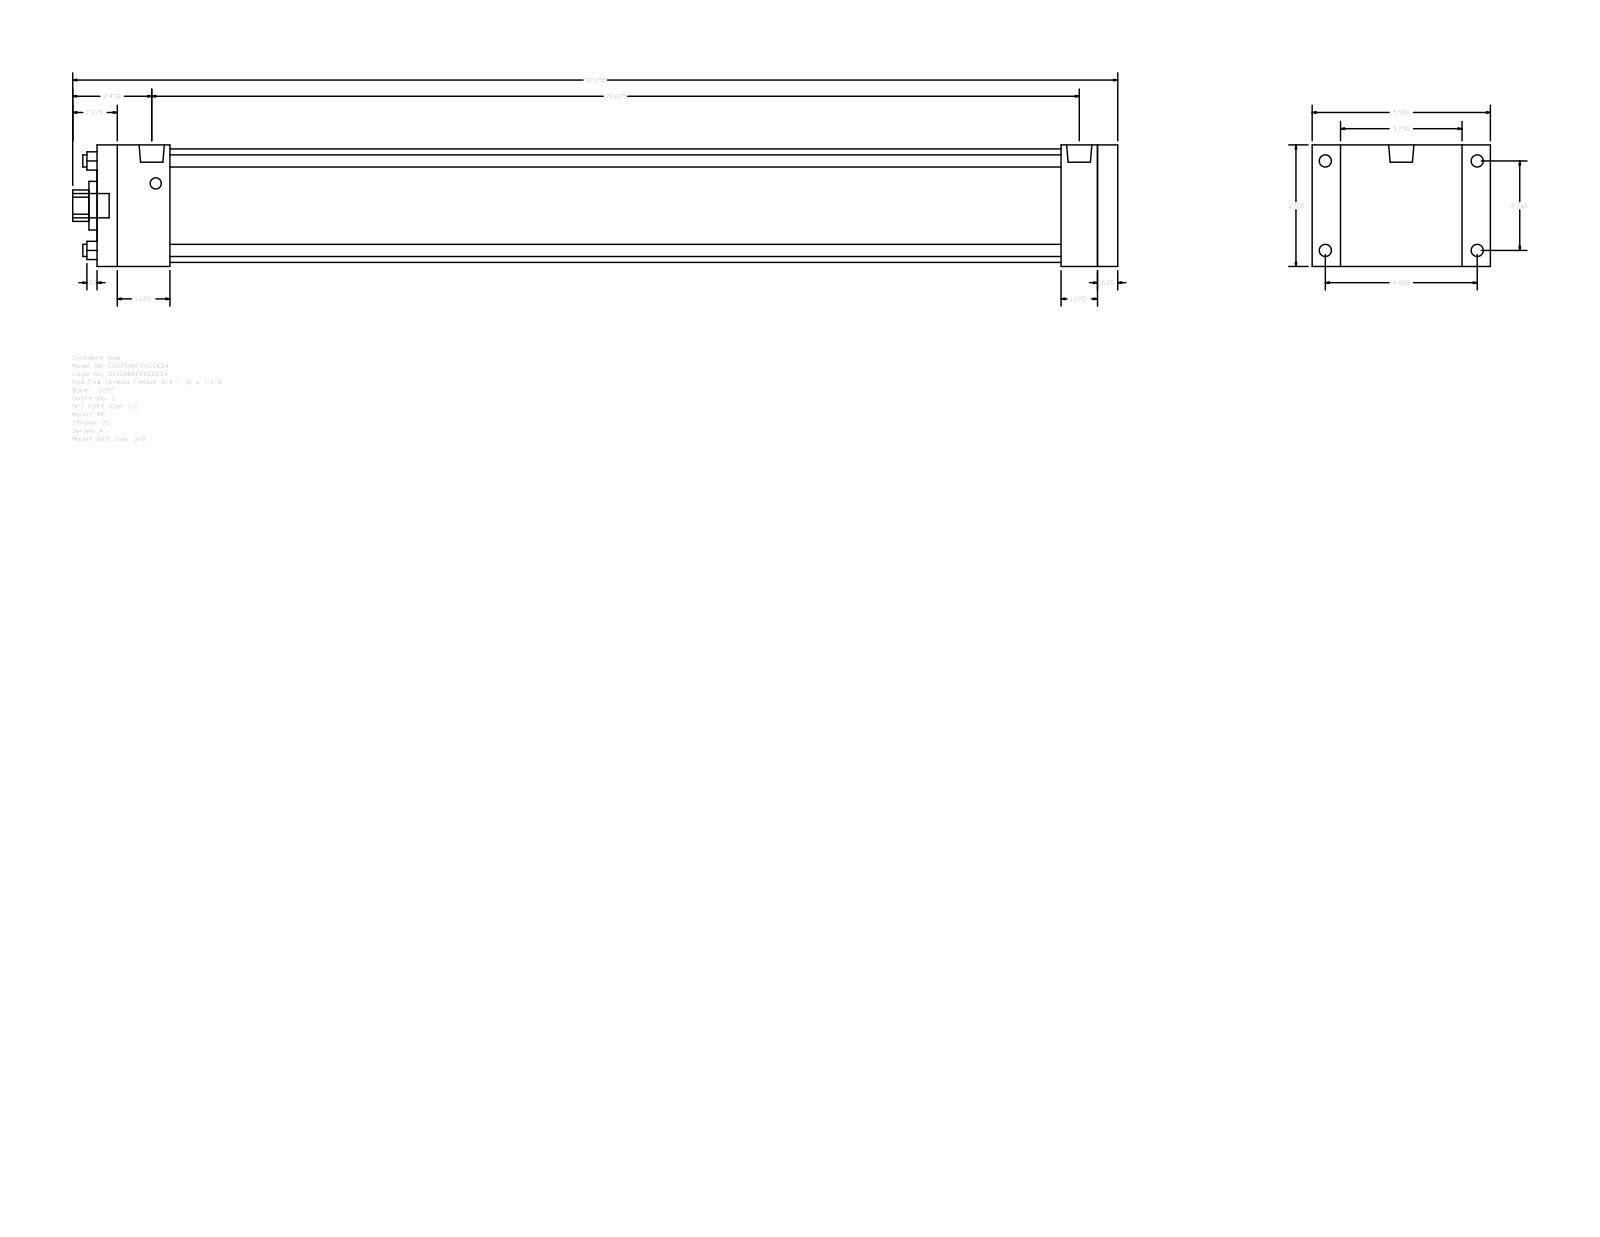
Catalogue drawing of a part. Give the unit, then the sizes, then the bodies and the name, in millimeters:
Units: millimetres
Overall size (bounding box): 819.15 × 139.7 × 95.25
Round holes (diameter × count): ⌀9.53 ×4, ⌀25.4 ×1, ⌀38.1 ×1, ⌀88.9 ×1
Round bosses / shafts (diameter × count): ⌀9.53 ×4, ⌀8.73 ×4, ⌀19.77 ×2, ⌀19.05 ×1
Partial cylindrical surfaces — rounded edges, fillets, slot ends (radius × count): R12.29 ×1
Main face-to-face distances: 95.24, 800.1, 784.22, 15.88, 22.23, 117.47, 28.57, 755.65, 44.45, 57.15
Hole centre spacings: 49.57, 70.1, 99.14
Bodies: 0 solids, 92 faces (64 planar, 28 cylindrical, 0 other)
Part name (STEP PRODUCT): A_RF__0325_1
STEP written by: GSSL Pune (CONFIG_CONTROL_DESIGN)
